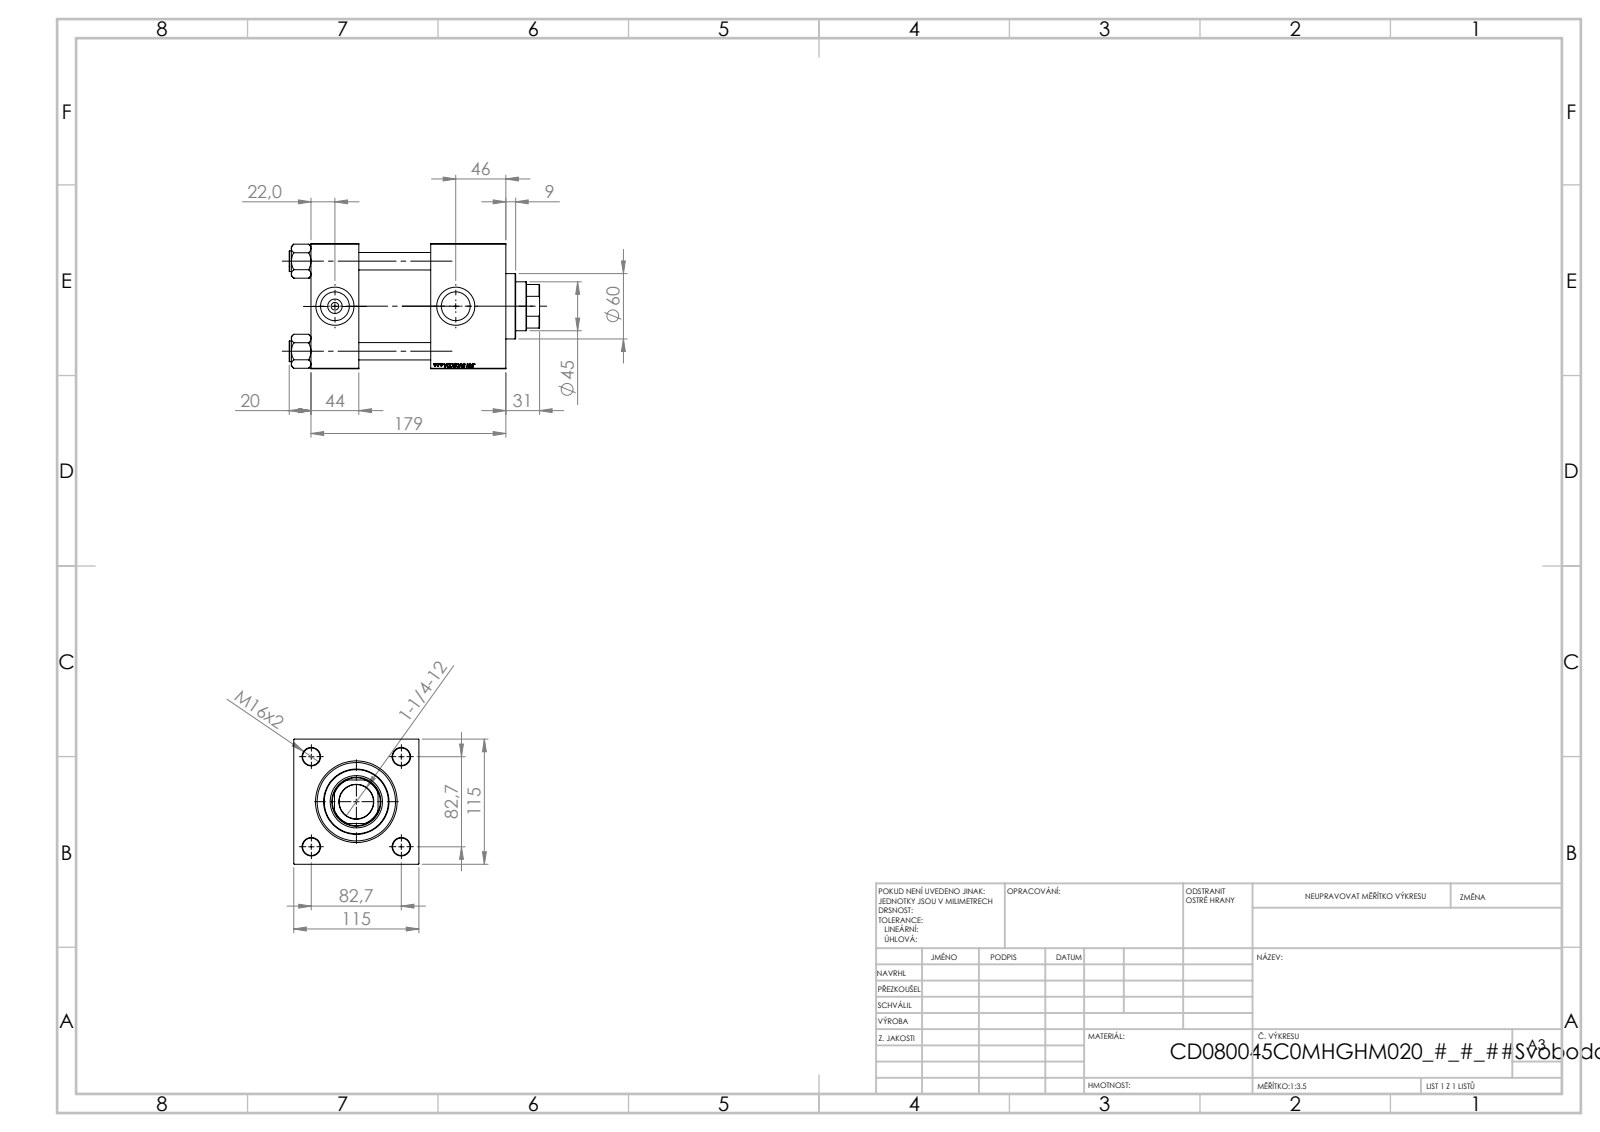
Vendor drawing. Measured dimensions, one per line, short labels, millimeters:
name: V215CD_VC_C; V215CD_VCP_C; V215CD_Body_C; NUT_M5_V215CD_C (+1 more)
written by: SolidWorks 2019 (CONFIG_CONTROL_DESIGN)
unit: mm
bodies: 11 solids, 1196 faces (574 planar, 86 cylindrical, 536 other)
size: 230 × 115 × 115
volume: 1 819 000 mm³; area: 273 876 mm²
holes: 4× ⌀16, 2× ⌀7, 2× ⌀26.44, 2× ⌀35, 1× ⌀31.5, 1× ⌀45, 1× ⌀48, 1× ⌀61, 1× ⌀72, 1× ⌀80
bosses: 4× ⌀19, 1× ⌀86, 1× ⌀60
rounds: 1× R22
face distances: 115, 44, 110, 179, 135, 66, 69, 20, 150.3, 106.3
hole spacings: 58.48, 82.7, 116.96, 111
